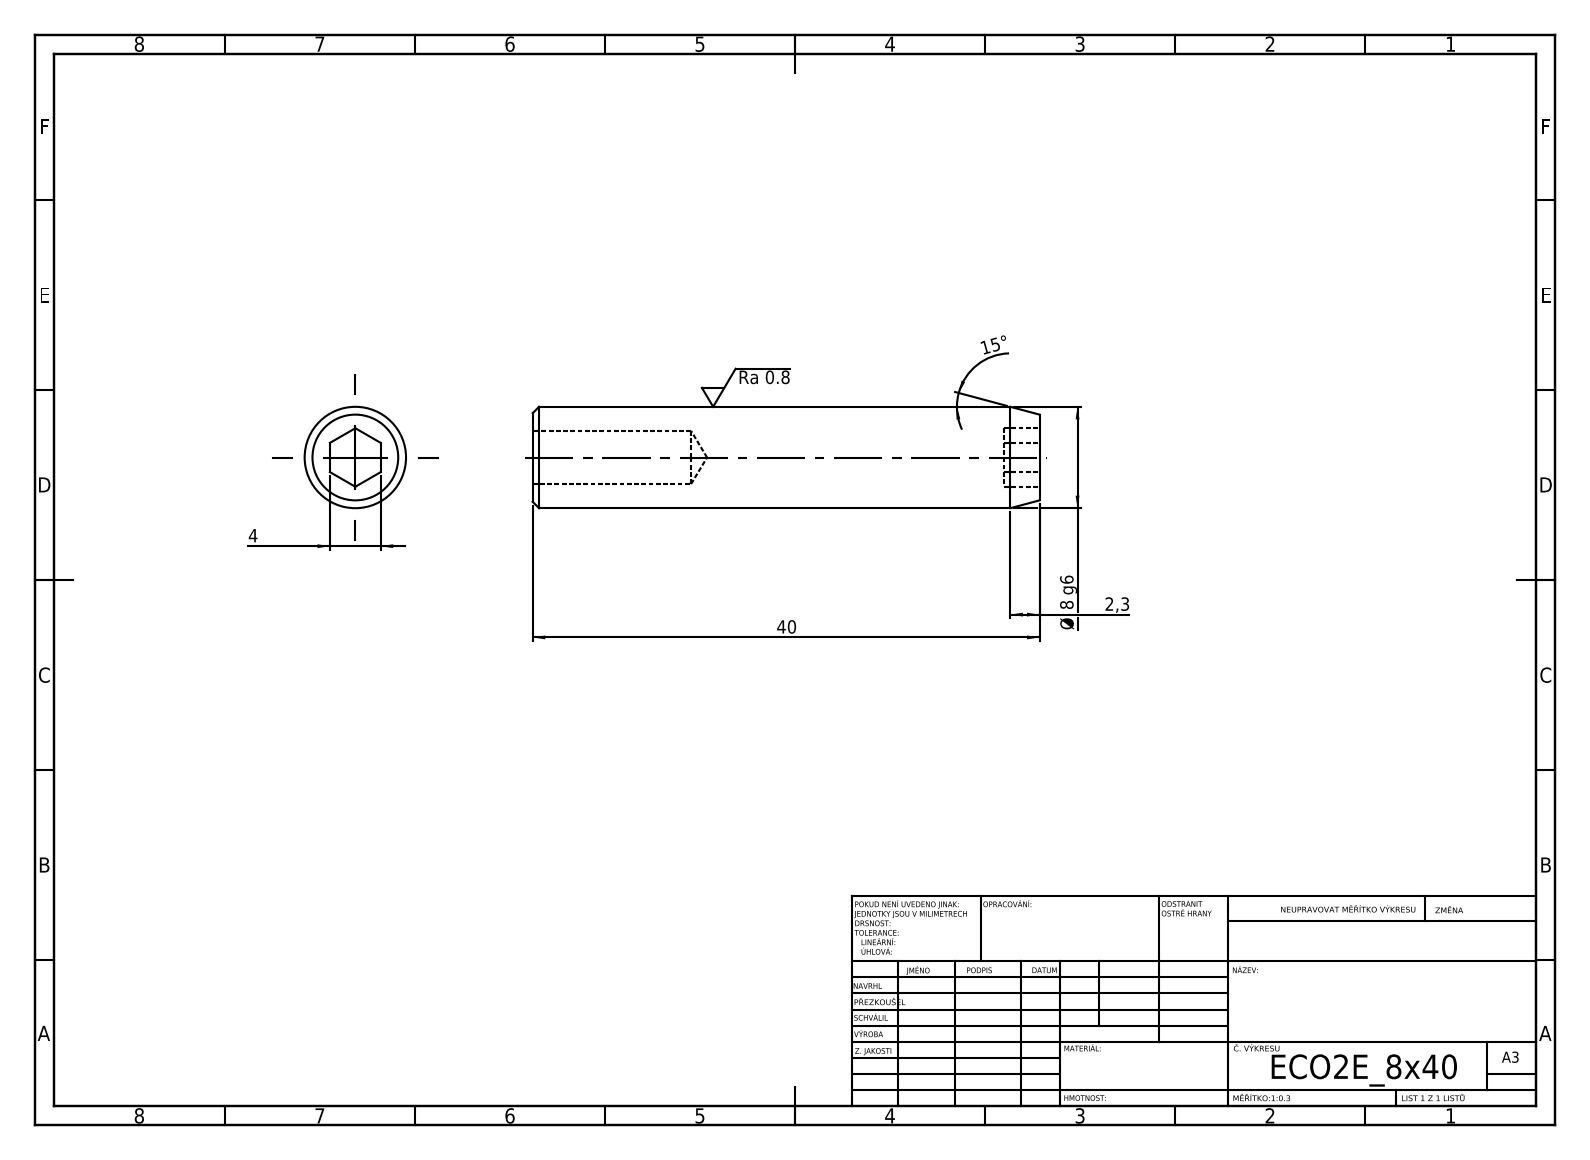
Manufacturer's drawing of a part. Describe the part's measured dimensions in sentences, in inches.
Its 3-D file was written by "SolidWorks 2019 (CONFIG_CONTROL_DESIGN)". It is 1 solid with 19 faces: 9 planar, 4 cylindrical and 6 other. Overall it measures 1.575 by 0.315 by 0.315 inches. Its volume is 0.108 cubic inches and its surface area 1.995 square inches. Round holes: 1 of diameter 0.165. Round bosses or shafts: 1 of diameter 0.315. The main face-to-face distances are 1.575, 0.157, 0.11, 1.465.
